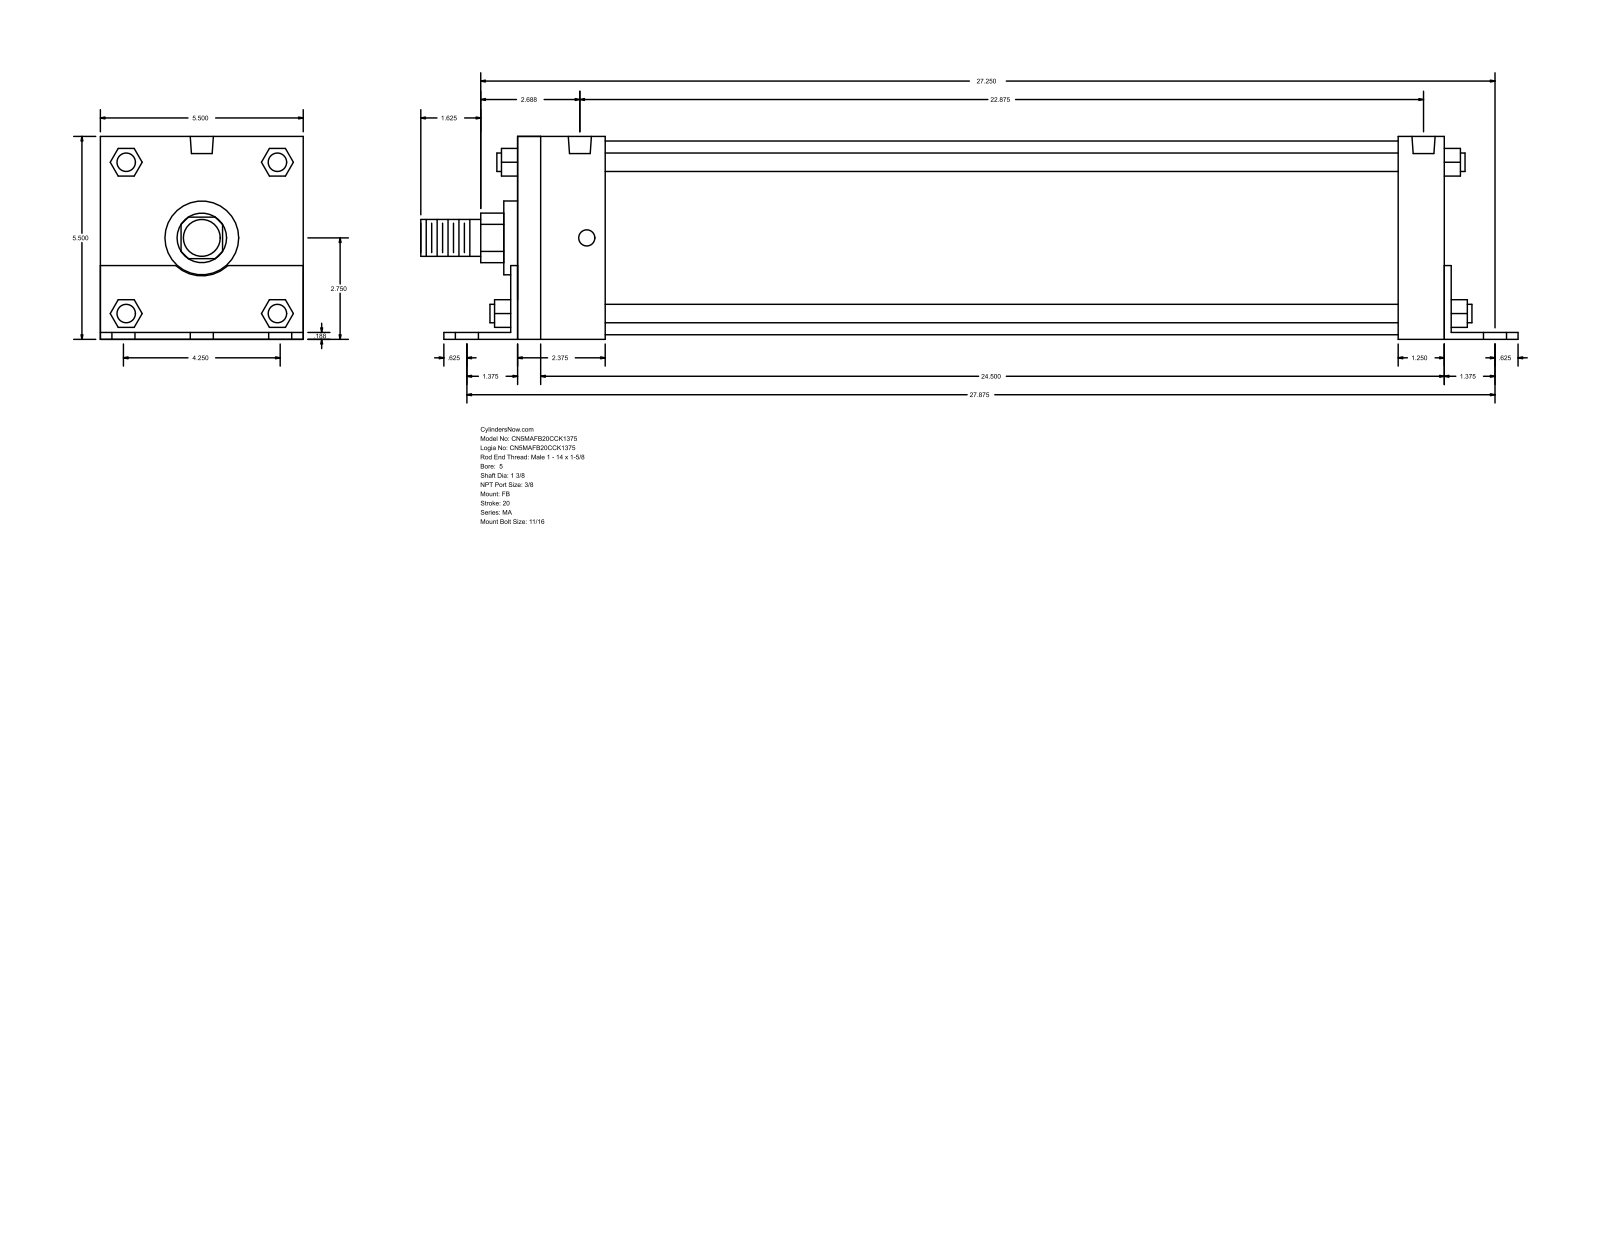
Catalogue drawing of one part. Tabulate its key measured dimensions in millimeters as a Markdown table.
| quantity | value |
| --- | --- |
| part name | MA_FB__0500_1.375 |
| STEP written by | GSSL Pune (CONFIG_CONTROL_DESIGN) |
| units | millimeters |
| bodies | 0 solids, 140 faces (105 planar, 35 cylindrical, 0 other) |
| overall size | 755.65 × 139.75 × 139.7 |
| round holes (diameter × count) | 17.46 × 6, 11.11 × 4, 15.93 × 2 |
| round bosses / shafts (diameter × count) | 12.7 × 4, 133.35 × 1, 50.8 × 1, 34.92 × 1, 25.4 × 1 |
| partial cylindrical surfaces (radius × count) | 17.06 × 1, 26.16 × 1 |
| main face-to-face distances | 139.7, 4.76, 139.75, 642.94, 4.71, 134.99, 638.18, 647.7, 31.75, 36.51 |
| hole center spacings | 53.98, 710.08, 708.03, 4.77, 73.04, 76.34, 94.68, 98.64 |
